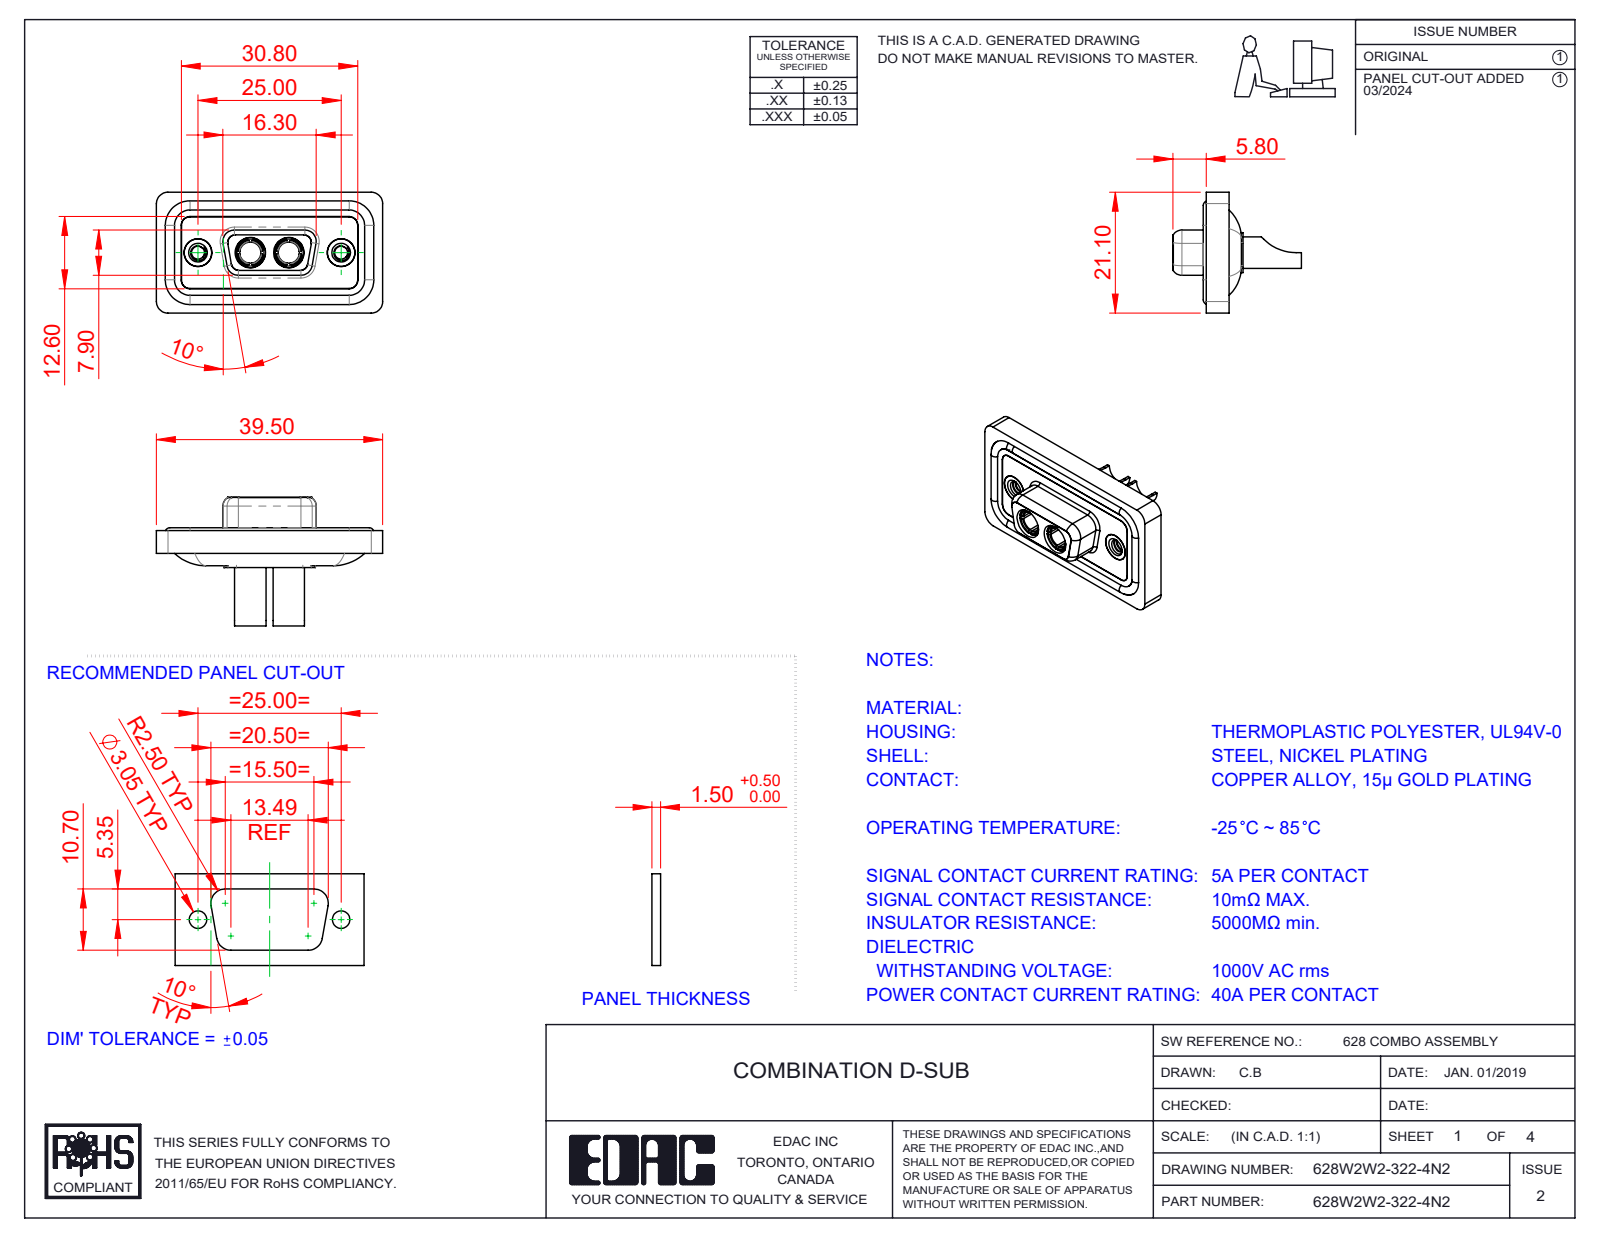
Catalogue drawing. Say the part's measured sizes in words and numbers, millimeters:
The part is named "628Combo Housing_2W2; 628Combo Waterproof Housing_09 Contacts; 628Combo Shell Front_09 Contacts; 628Combo Shell Rear_09 Contacts (+3 more)". Its 3-D file was written by "SolidWorks 2023 (CONFIG_CONTROL_DESIGN)". It is 11 solids with 540 faces: 167 planar, 236 cylindrical and 137 other. Overall it measures 39.5 by 22.45 by 21.1 millimeters. Its volume is 4 793 cubic millimeters and its surface area 7 916 square millimeters. Round holes: 4 of diameter 4.85, 2 of diameter 2.26, 2 of diameter 3.7, 2 of diameter 4, 2 of diameter 4.05, 2 of diameter 4.6, 2 of diameter 5, 2 of diameter 5.3. Round bosses or shafts: 4 of diameter 1.6, 2 of diameter 5.5, 2 of diameter 5.2, 2 of diameter 4.96, 2 of diameter 4.95, 2 of diameter 4.8, 2 of diameter 4.75, 2 of diameter 3.75. Partial cylindrical surfaces (rounded edges, fillets, slot ends): 22 of radius 1.5, 18 of radius 2, 8 of radius 1.35, 8 of radius 1.6, 4 of radius 0.25, 4 of radius 0.5, 4 of radius 0.6, 4 of radius 0.65. The main face-to-face distances are 0.4, 1.1, 2.9, 1.8, 0.5, 1.6, 5.65, 7.45, 5.35, 3.1. The hole center spacings are 9.14, 15.86, 6.72, 25.
